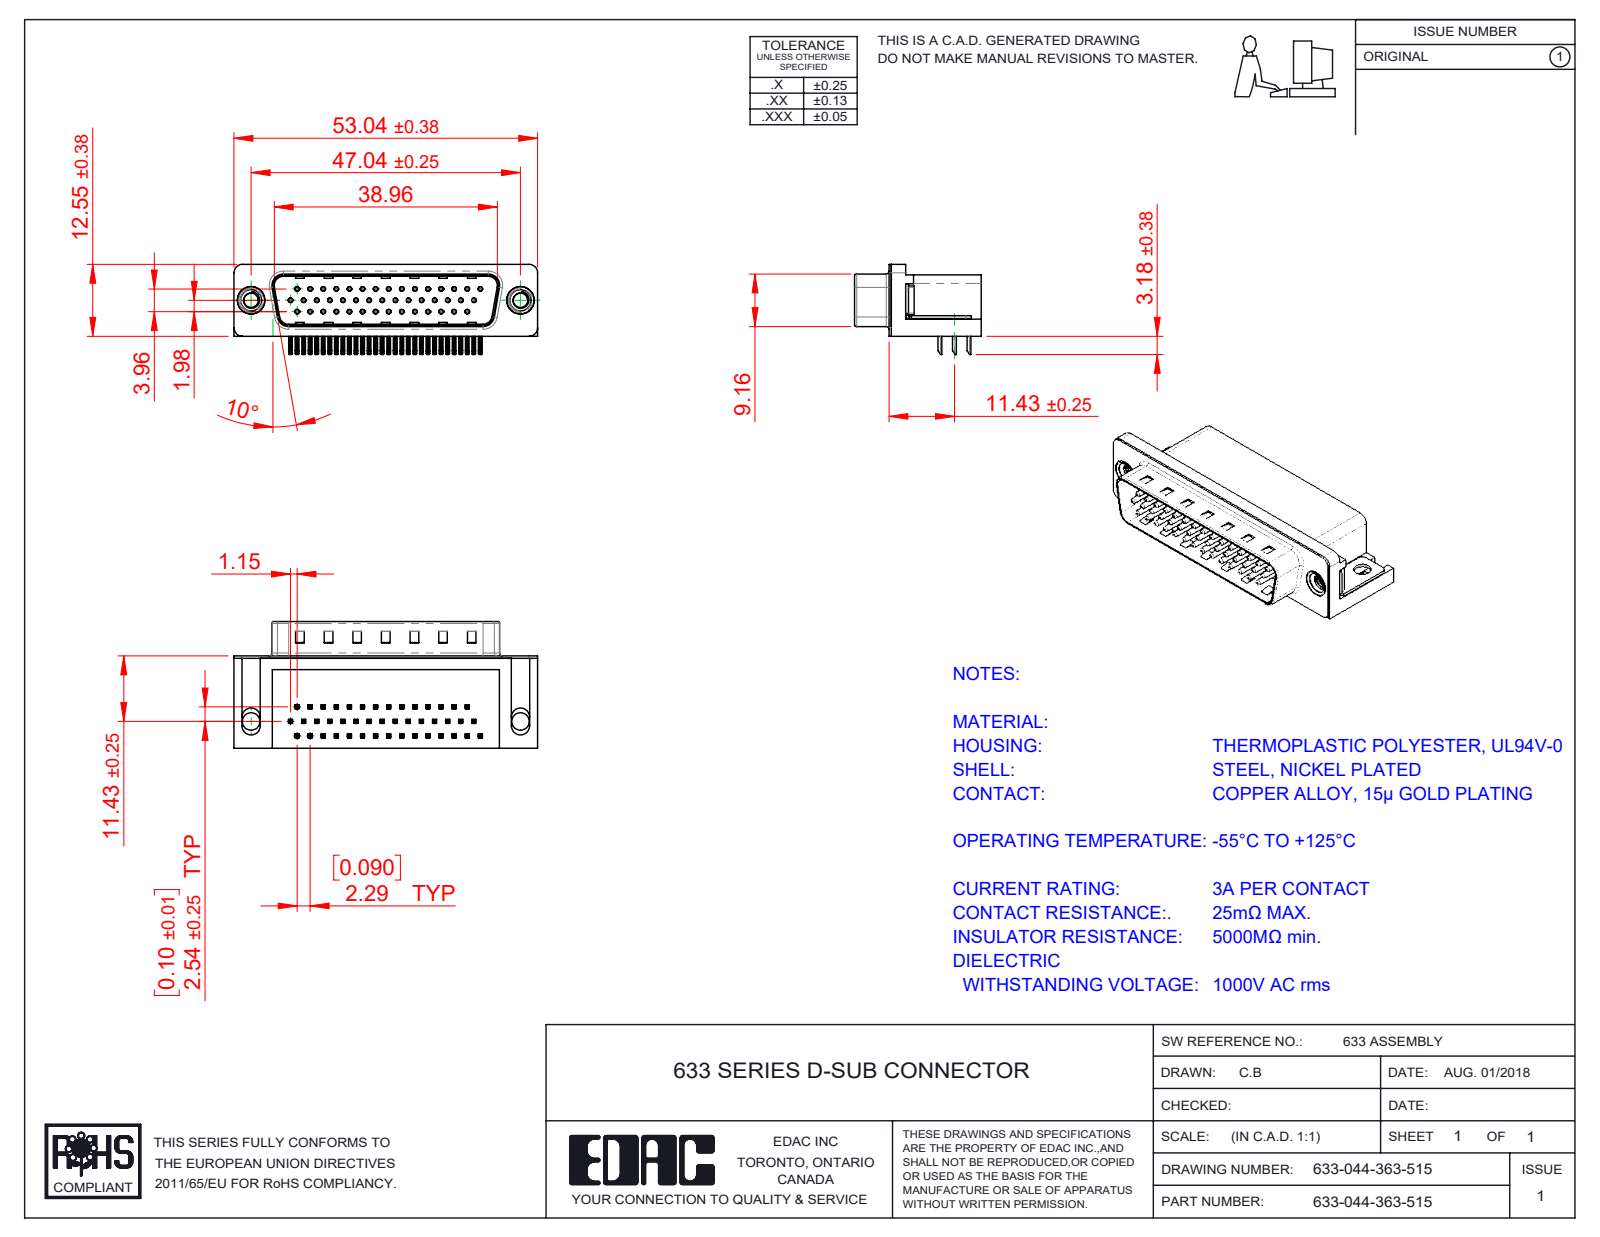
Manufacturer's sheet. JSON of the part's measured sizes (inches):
{"part_name": "633 M3 Threaded Rivet; 633-044-363-515; 633 Contact Top; 633 Thru Hole Board Mount (+4 more)", "step_written_by": "SolidWorks 2016 (CONFIG_CONTROL_DESIGN)", "units": "inches", "bodies": {"solids": 50, "faces": 3688, "planar": 2315, "cylindrical": 1064, "other": 309}, "overall_size": [2.088, 0.87, 0.619], "volume_in3": 0.495, "surface_area_in2": 15.82, "round_holes": [[0.014, 44], [0.031, 44], [0.098, 2], [0.12, 2], [0.157, 2], [0.189, 2], [0.197, 2]], "round_bosses_or_shafts": [[0.03, 44], [0.193, 2], [0.187, 2], [0.154, 2]], "partial_cylinders_radius": [[0.01, 184], [0.005, 88], [0.039, 16], [0.02, 9], [0.063, 8], [0.059, 7], [0.035, 4], [0.079, 4]], "face_to_face_distances": [0.016, 0.407, 0.618, 0.114, 0.345, 0.098, 0.083, 0.634, 0.421, 0.1], "hole_center_spacings": [0.09, 0.18, 0.18, 0.09, 0.27, 0.361, 0.451, 0.089]}
